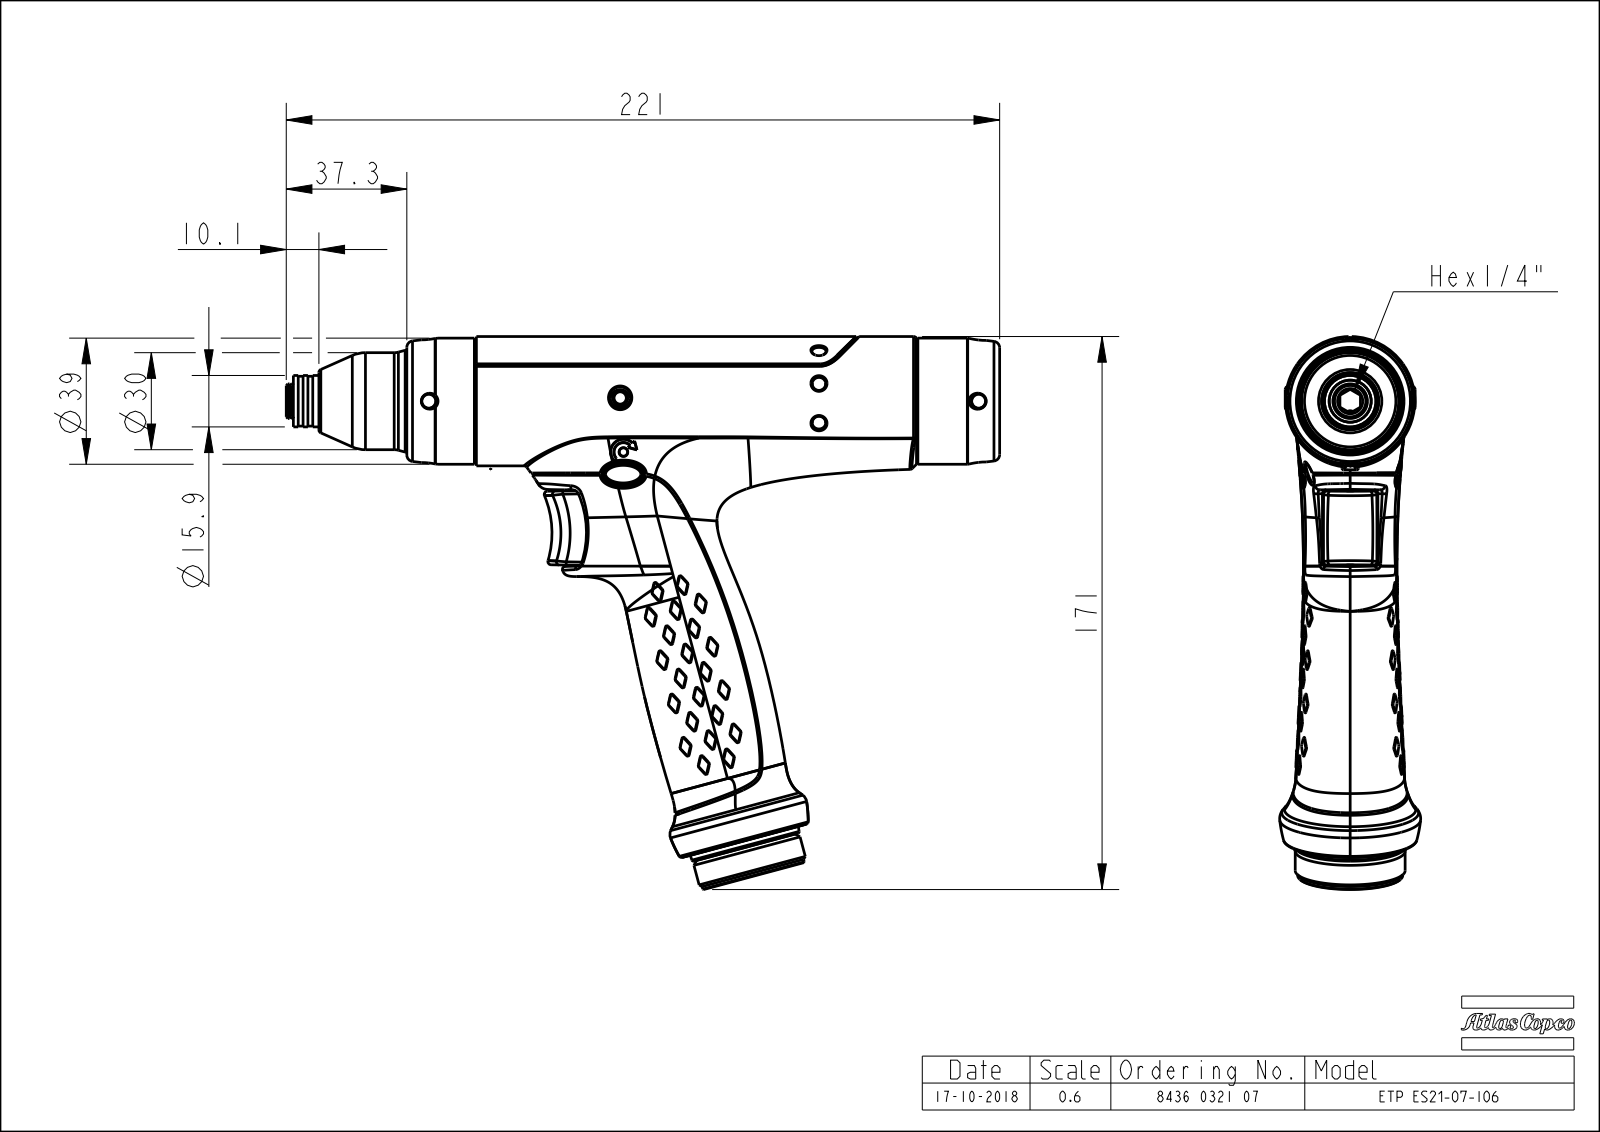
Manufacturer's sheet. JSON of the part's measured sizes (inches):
{"part_name": "EXT_COMP_SW0002", "step_written_by": "CREO PARAMETRIC BY PTC INC, 2020281 (CONFIG_CONTROL_DESIGN)", "units": "inches", "bodies": {"solids": 2, "faces": 956, "planar": 103, "cylindrical": 123, "other": 730}, "overall_size": [8.689, 6.732, 1.717], "volume_in3": 23.56, "surface_area_in2": 76.29, "round_holes": [[0.177, 5], [0.15, 1], [0.512, 1], [1.154, 1]], "round_bosses_or_shafts": [[1.575, 1], [1.535, 1], [1.339, 1], [1.28, 1], [1.24, 1], [1.181, 1], [0.626, 1], [0.606, 1]], "partial_cylinders_radius": [[0.039, 9], [0.011, 6], [0.02, 6], [0.089, 6], [0.016, 4], [0.02, 4], [0.047, 4], [0.008, 2]], "face_to_face_distances": [4.972, 0.941, 2.789, 1.848, 3.969, 1.004, 3.945, 0.024, 1.028, 0.747], "hole_center_spacings": [6.697, 2.331, 4.366]}
